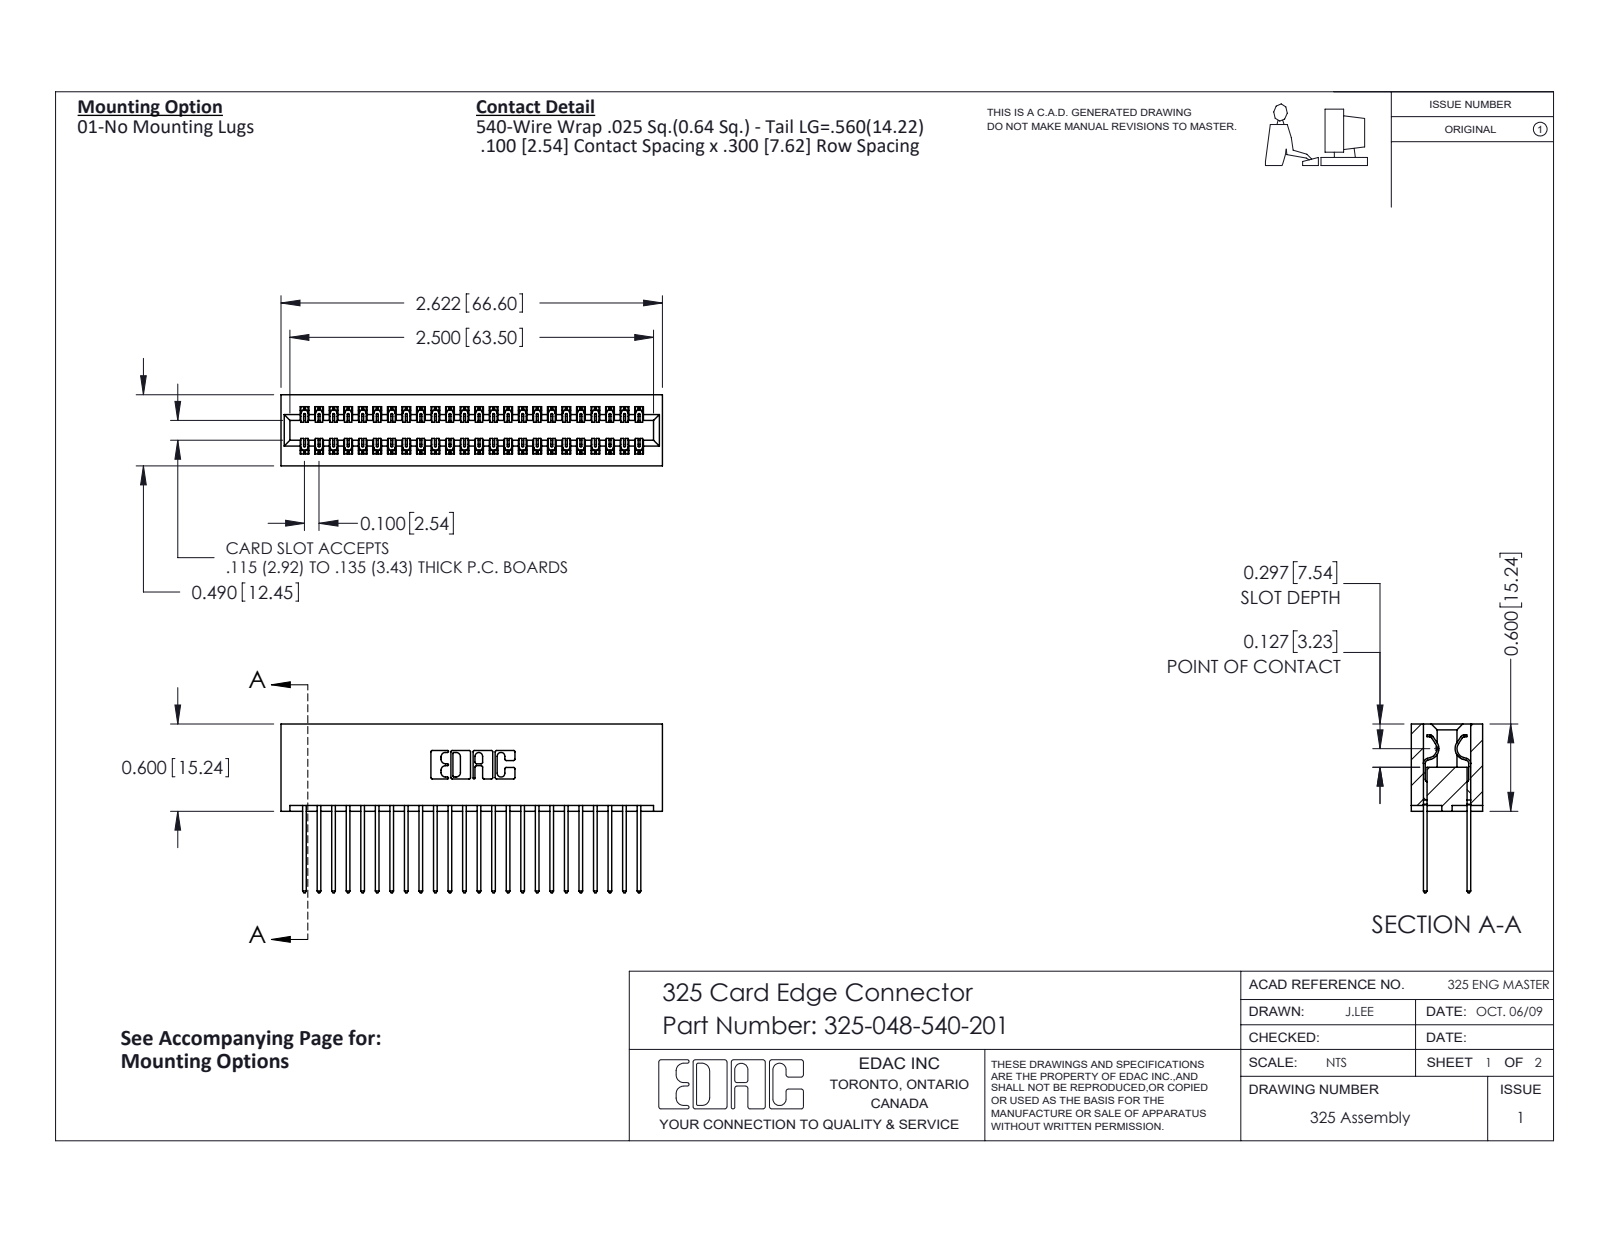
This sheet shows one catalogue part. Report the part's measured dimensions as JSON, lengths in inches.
{"part_name": "325-292-001_325-293-140; 325-048-540-201; 325 Part_Lugless", "step_written_by": "SolidWorks 2016 (CONFIG_CONTROL_DESIGN)", "units": "inches", "bodies": {"solids": 49, "faces": 2602, "planar": 1794, "cylindrical": 808, "other": 0}, "overall_size": [2.622, 1.16, 0.49], "volume_in3": 0.563, "surface_area_in2": 19.01, "partial_cylinders_radius": [[0.006, 72], [0.01, 48], [0.01, 22], [0.007, 6], [0.031, 6], [0.026, 3], [0.014, 2], [0.022, 2]], "face_to_face_distances": [0.083, 0.407, 0.3, 0.107, 0.383, 0.025, 0.325, 0.49, 0.275, 0.56]}
